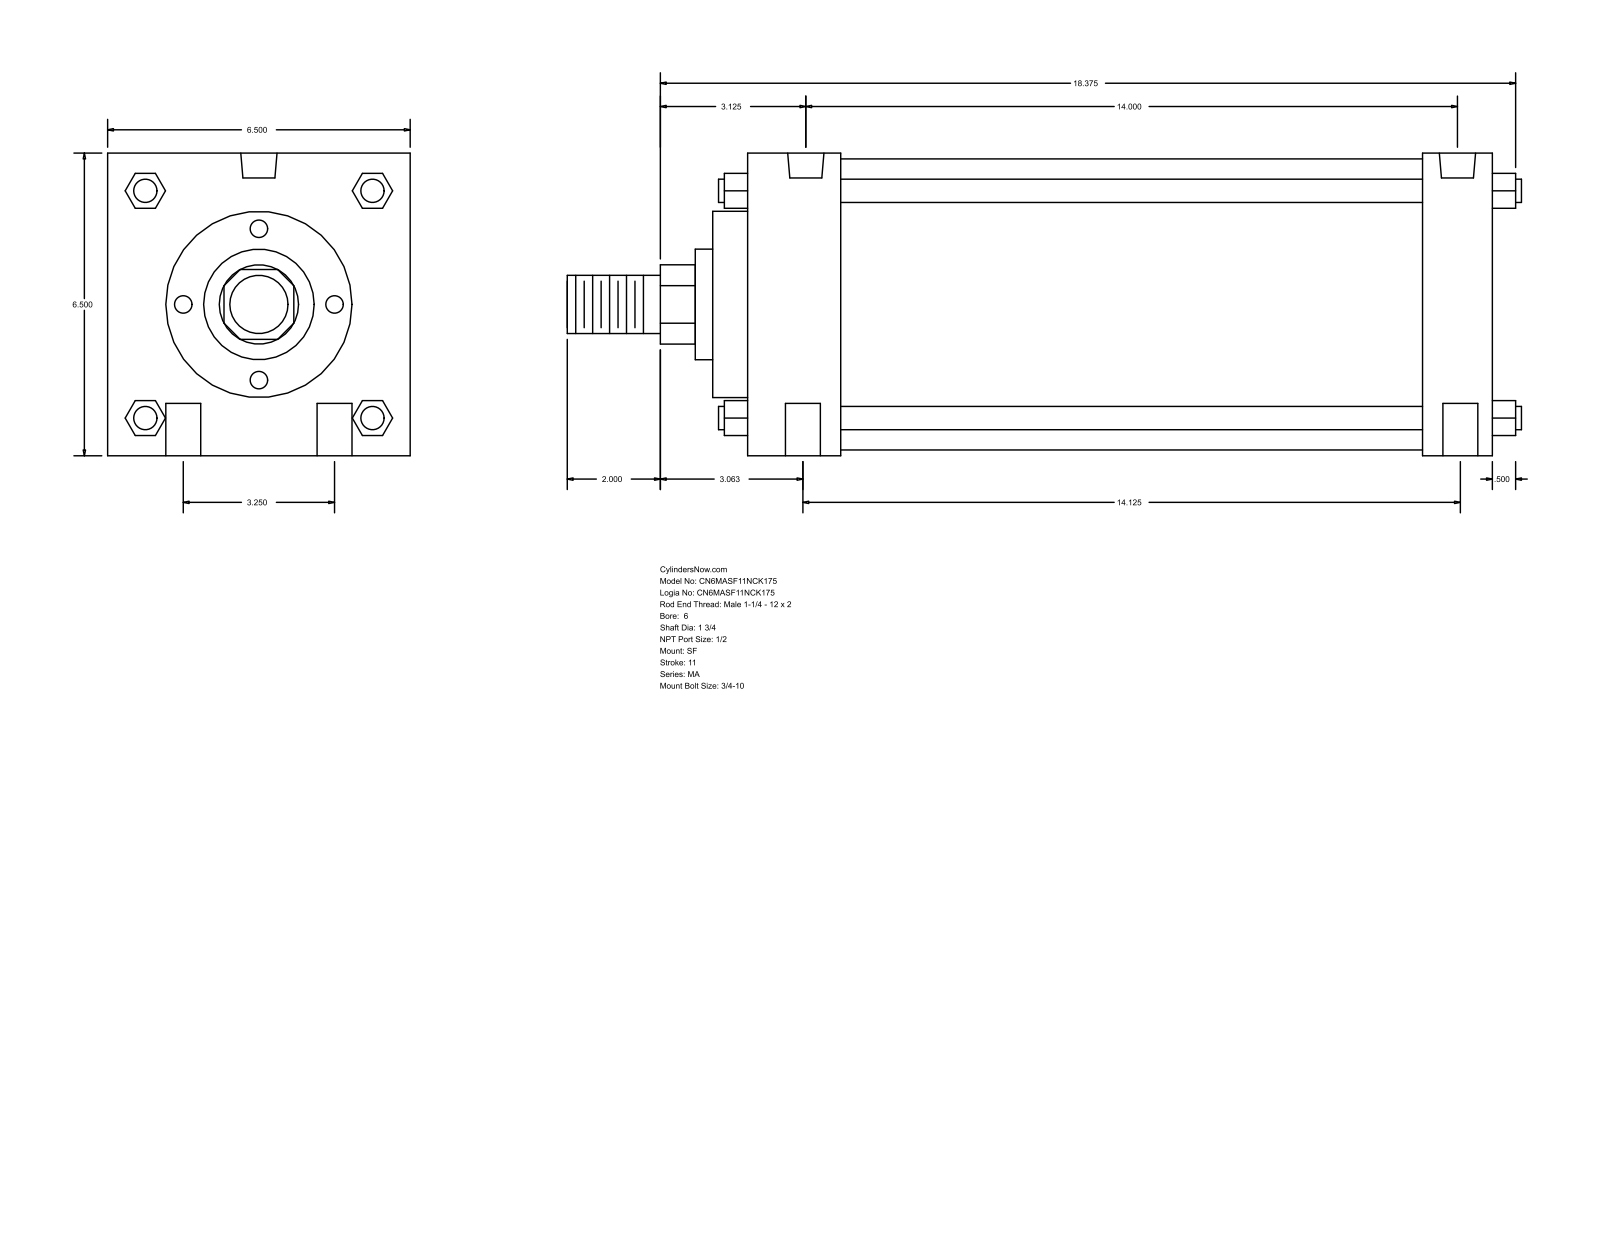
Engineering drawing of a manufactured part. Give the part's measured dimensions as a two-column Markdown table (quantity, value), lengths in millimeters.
| quantity | value |
| --- | --- |
| part name | MA_SF__0600_1.75 |
| STEP written by | GSSL Pune (CONFIG_CONTROL_DESIGN) |
| units | millimeters |
| bodies | 0 solids, 126 faces (95 planar, 31 cylindrical, 0 other) |
| overall size | 520.7 × 165.1 × 165.1 |
| round holes (diameter × count) | 19.05 × 4, 17.46 × 2, 19.77 × 2 |
| round bosses / shafts (diameter × count) | 12.7 × 4, 158.75 × 1, 101.6 × 1, 60.33 × 1, 44.45 × 1, 31.75 × 1 |
| partial cylindrical surfaces (radius × count) | 21.63 × 1 |
| main face-to-face distances | 165.1, 406.4, 19.05, 50.8, 368.31, 38.09, 317.51, 355.6, 69.85, 387.36 |
| hole center spacings | 41.3, 82.54, 355.6, 358.77, 359.56, 359.57, 368.14 |
